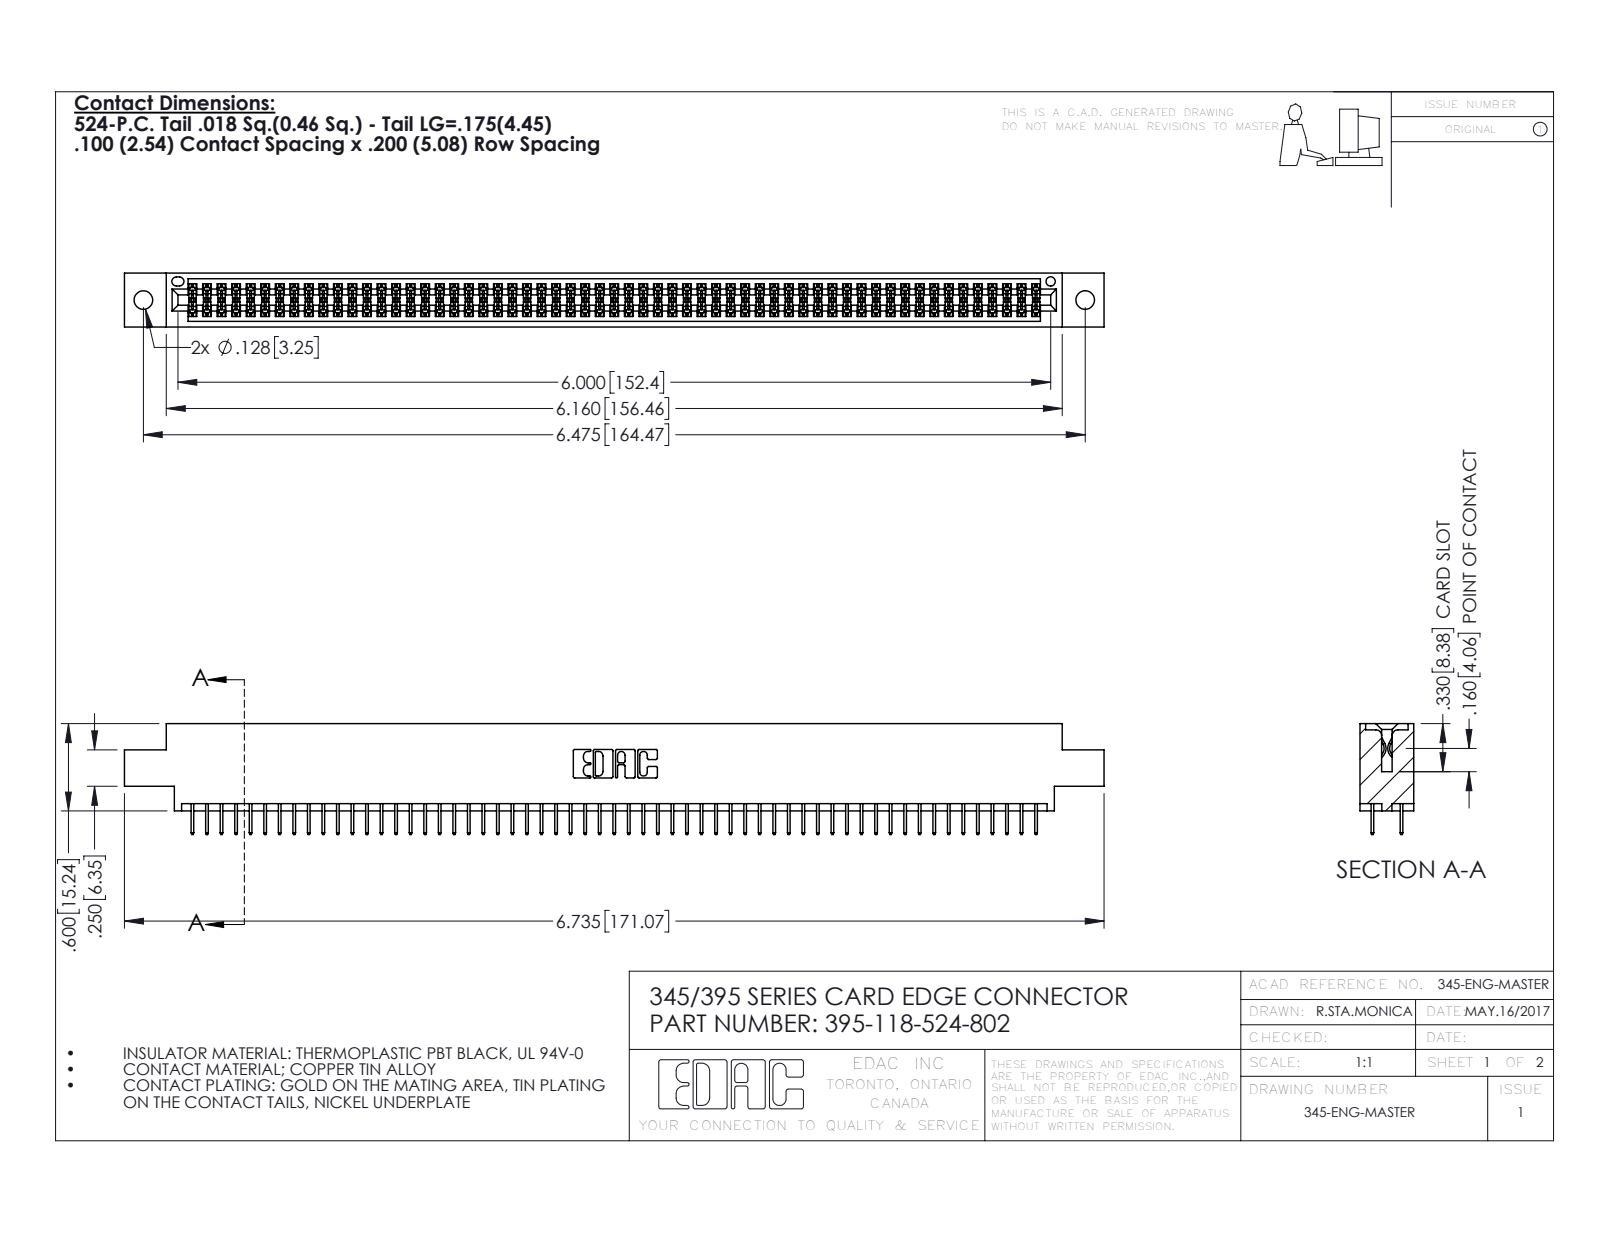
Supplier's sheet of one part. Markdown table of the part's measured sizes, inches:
| quantity | value |
| --- | --- |
| part name | 395-118-524-802; 345-292-001_345-293-124; 345 Part_0.170 Offset - 0.128 Dia |
| STEP written by | SolidWorks 2016 (CONFIG_CONTROL_DESIGN) |
| units | inches |
| bodies | 119 solids, 6502 faces (4686 planar, 1816 cylindrical, 0 other) |
| overall size | 6.735 × 0.762 × 0.37 |
| volume | 1.004 in³ |
| surface area | 37.26 in² |
| round holes (diameter × count) | 0.128 × 2, 0.064 × 1 |
| partial cylindrical surfaces (radius × count) | 0.006 × 177, 0.01 × 22, 0.007 × 6, 0.031 × 6, 0.026 × 3, 0.014 × 2, 0.019 × 2, 0.022 × 2 |
| main face-to-face distances | 0.072, 0.298, 0.37, 0.2, 0.098, 0.272, 0.025, 0.225, 0.072, 0.175 |
| hole center spacings | 0.27, 6.239, 6.475 |
